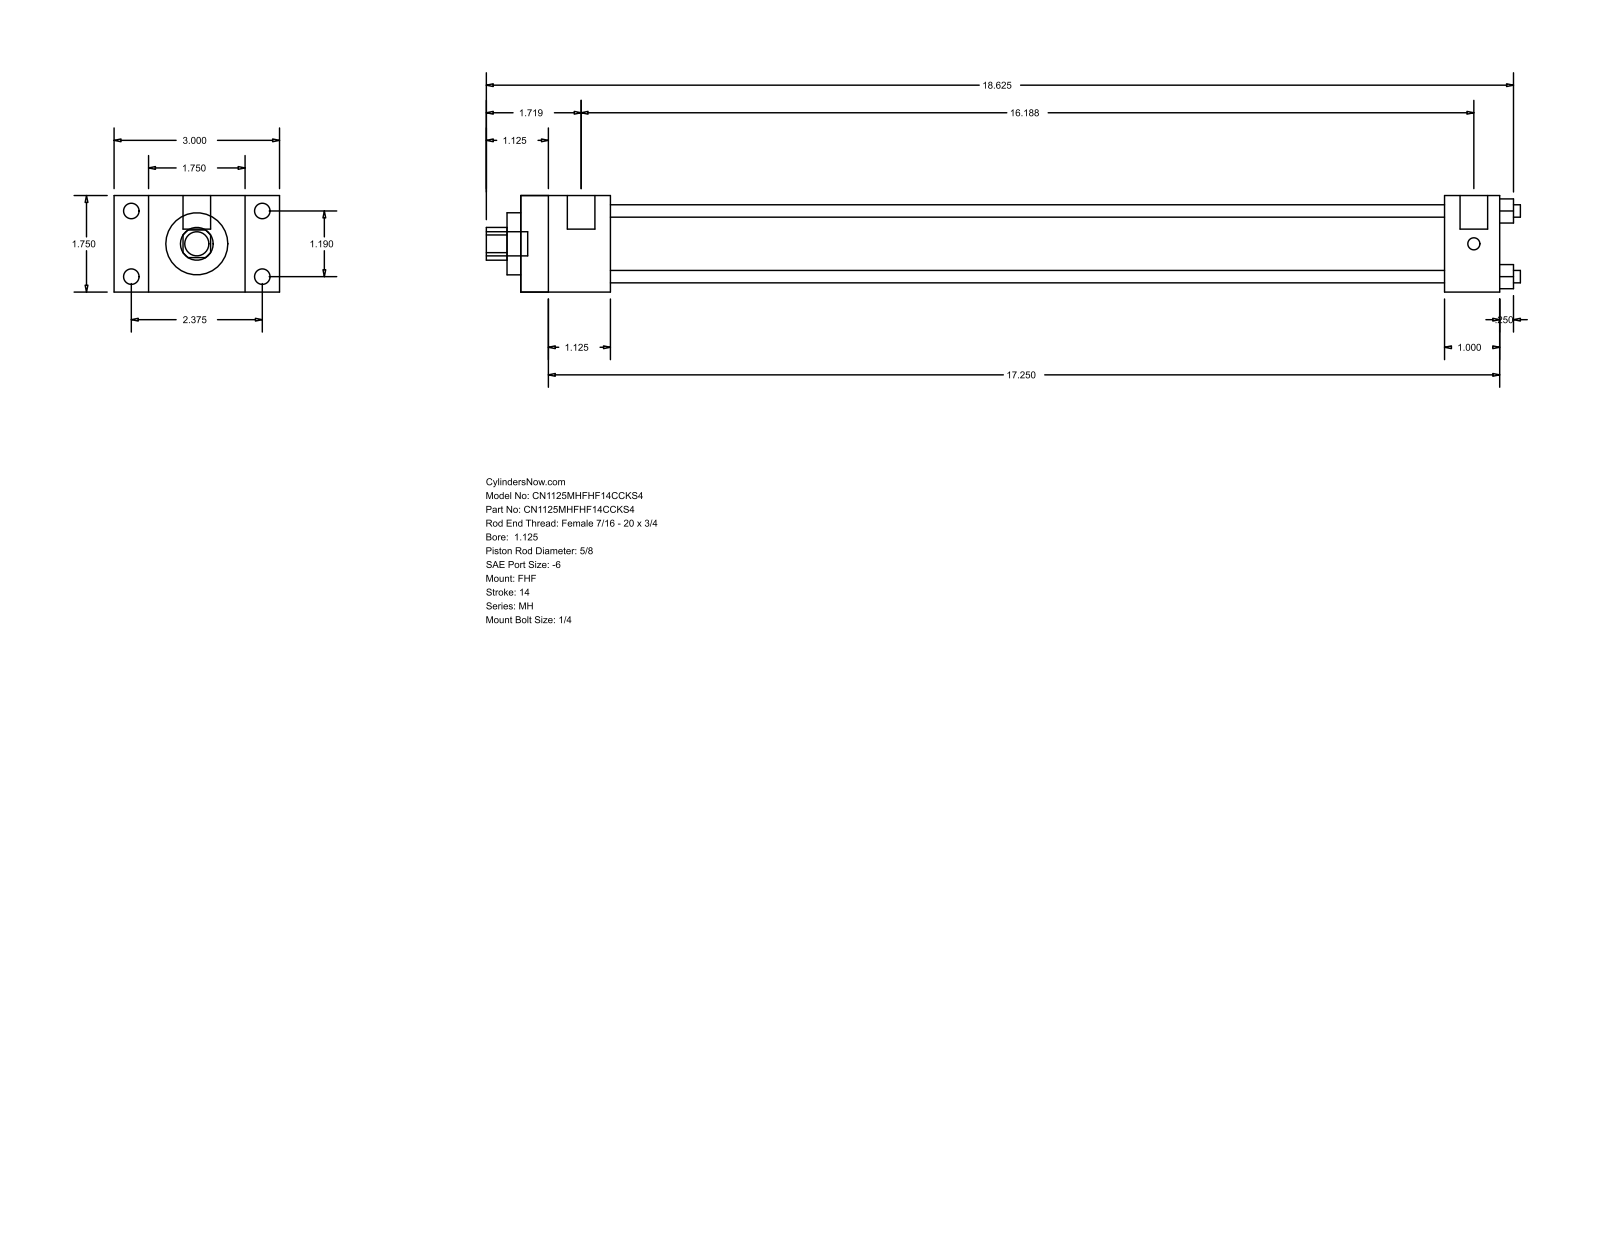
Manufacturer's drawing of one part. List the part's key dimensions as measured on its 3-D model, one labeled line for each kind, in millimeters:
Part name (STEP PRODUCT): MH_FHF__0112_0.625
STEP written by: GSSL Pune (CONFIG_CONTROL_DESIGN)
Units: millimetres
Bodies: 0 solids, 88 faces (60 planar, 28 cylindrical, 0 other)
Overall size (bounding box): 476.25 × 76.2 × 44.45
Round holes (diameter × count): ⌀5.71 ×4, ⌀15.88 ×1, ⌀28.57 ×1, ⌀34.92 ×1
Round bosses / shafts (diameter × count): ⌀7.14 ×4, ⌀5.56 ×4, ⌀12.7 ×2, ⌀11.11 ×1
Partial cylindrical surfaces — rounded edges, fillets, slot ends (radius × count): R7.54 ×1
Main face-to-face distances: 44.46, 15.87, 60.33, 41.27, 76.2, 450.85, 409.58, 425.44, 384.17, 25.41
Hole centre spacings: 21.37, 30.22, 42.74
